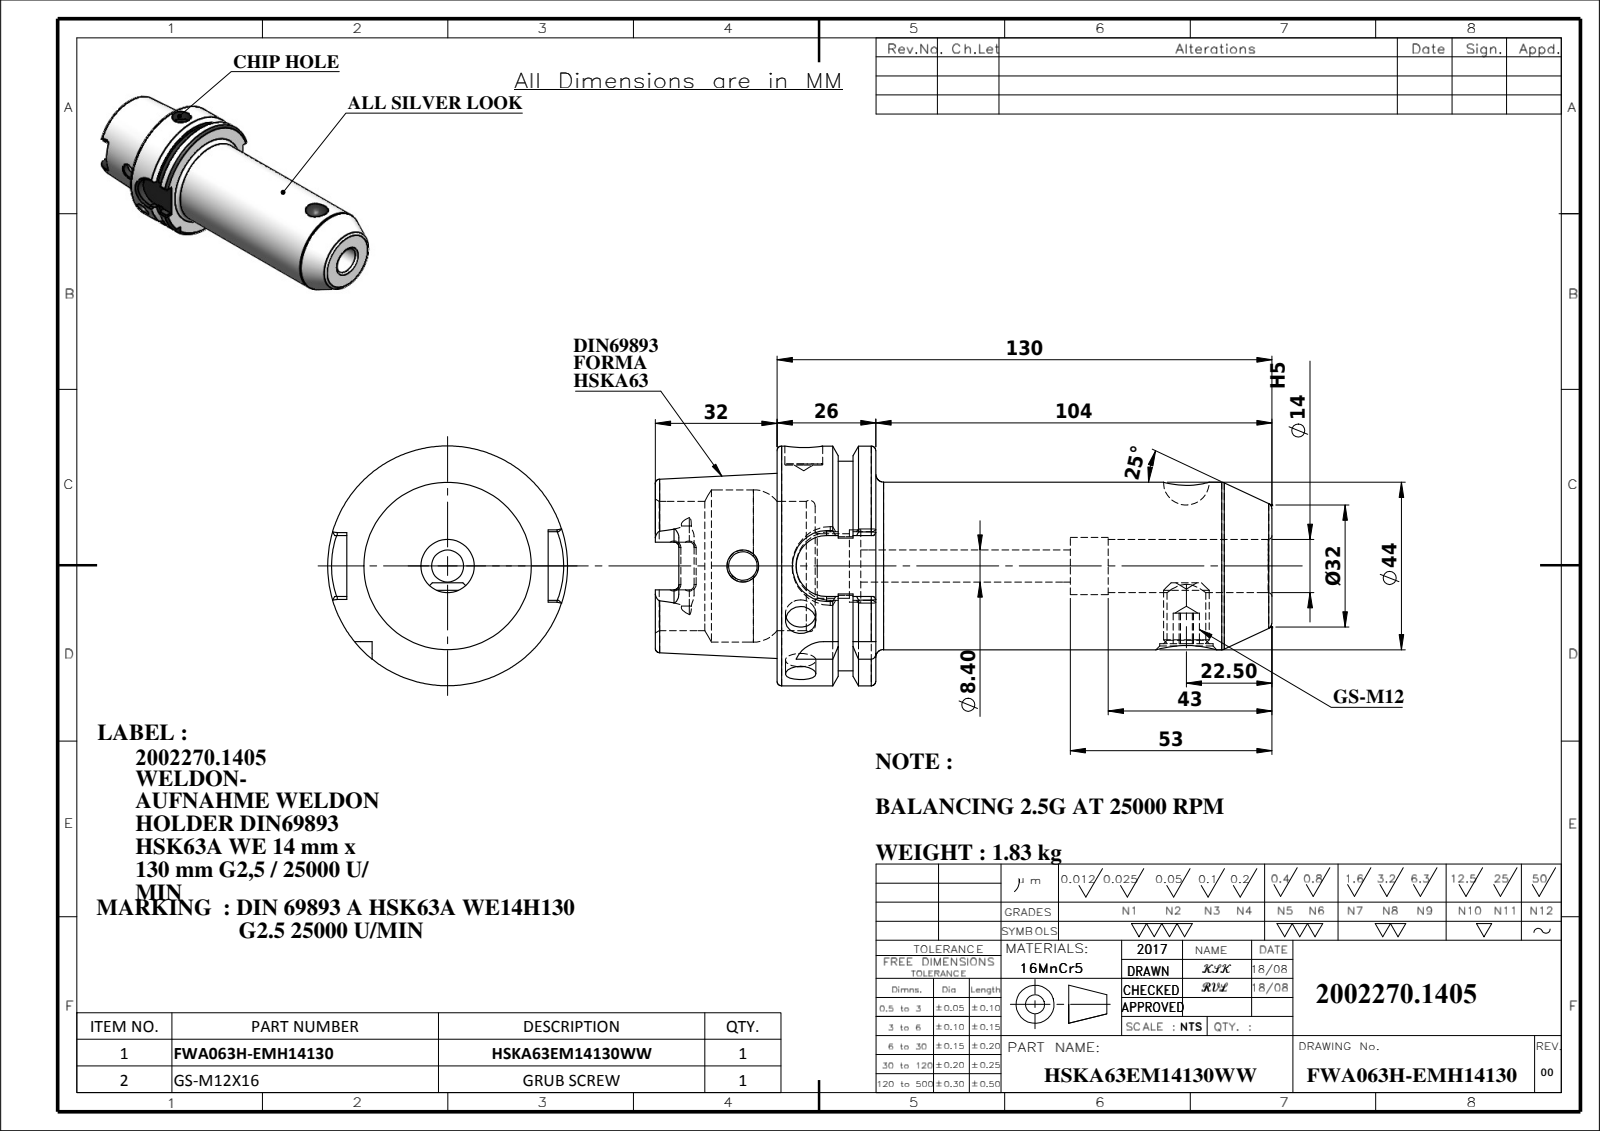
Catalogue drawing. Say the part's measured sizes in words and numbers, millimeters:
The part is named "HSKA63EM14130WW; GS-M12X16-DIN1835-B; 9163A-WE814130". Its 3-D file was written by "SolidWorks 2018 (CONFIG_CONTROL_DESIGN)". It is 2 solids with 203 faces: 66 planar, 57 cylindrical and 80 other. Overall it measures 162 by 63 by 63 millimeters. Its volume is 222 706 cubic millimeters and its surface area 40 855 square millimeters. Round holes: 2 of diameter 8, 2 of diameter 14, 1 of diameter 7.5, 1 of diameter 8.4, 1 of diameter 10, 1 of diameter 10.2, 1 of diameter 15, 1 of diameter 17, 1 of diameter 19, 1 of diameter 34, 1 of diameter 40. Round bosses or shafts: 1 of diameter 63, 1 of diameter 55, 1 of diameter 44, 1 of diameter 12. Partial cylindrical surfaces (rounded edges, fillets, slot ends): 6 of radius 1.3, 4 of radius 2.88, 2 of radius 8, 1 of radius 9. The main face-to-face distances are 25.95, 10, 15.95, 130, 120, 104.05, 32, 42, 57.95, 162. The hole center spacings are 100.5.
